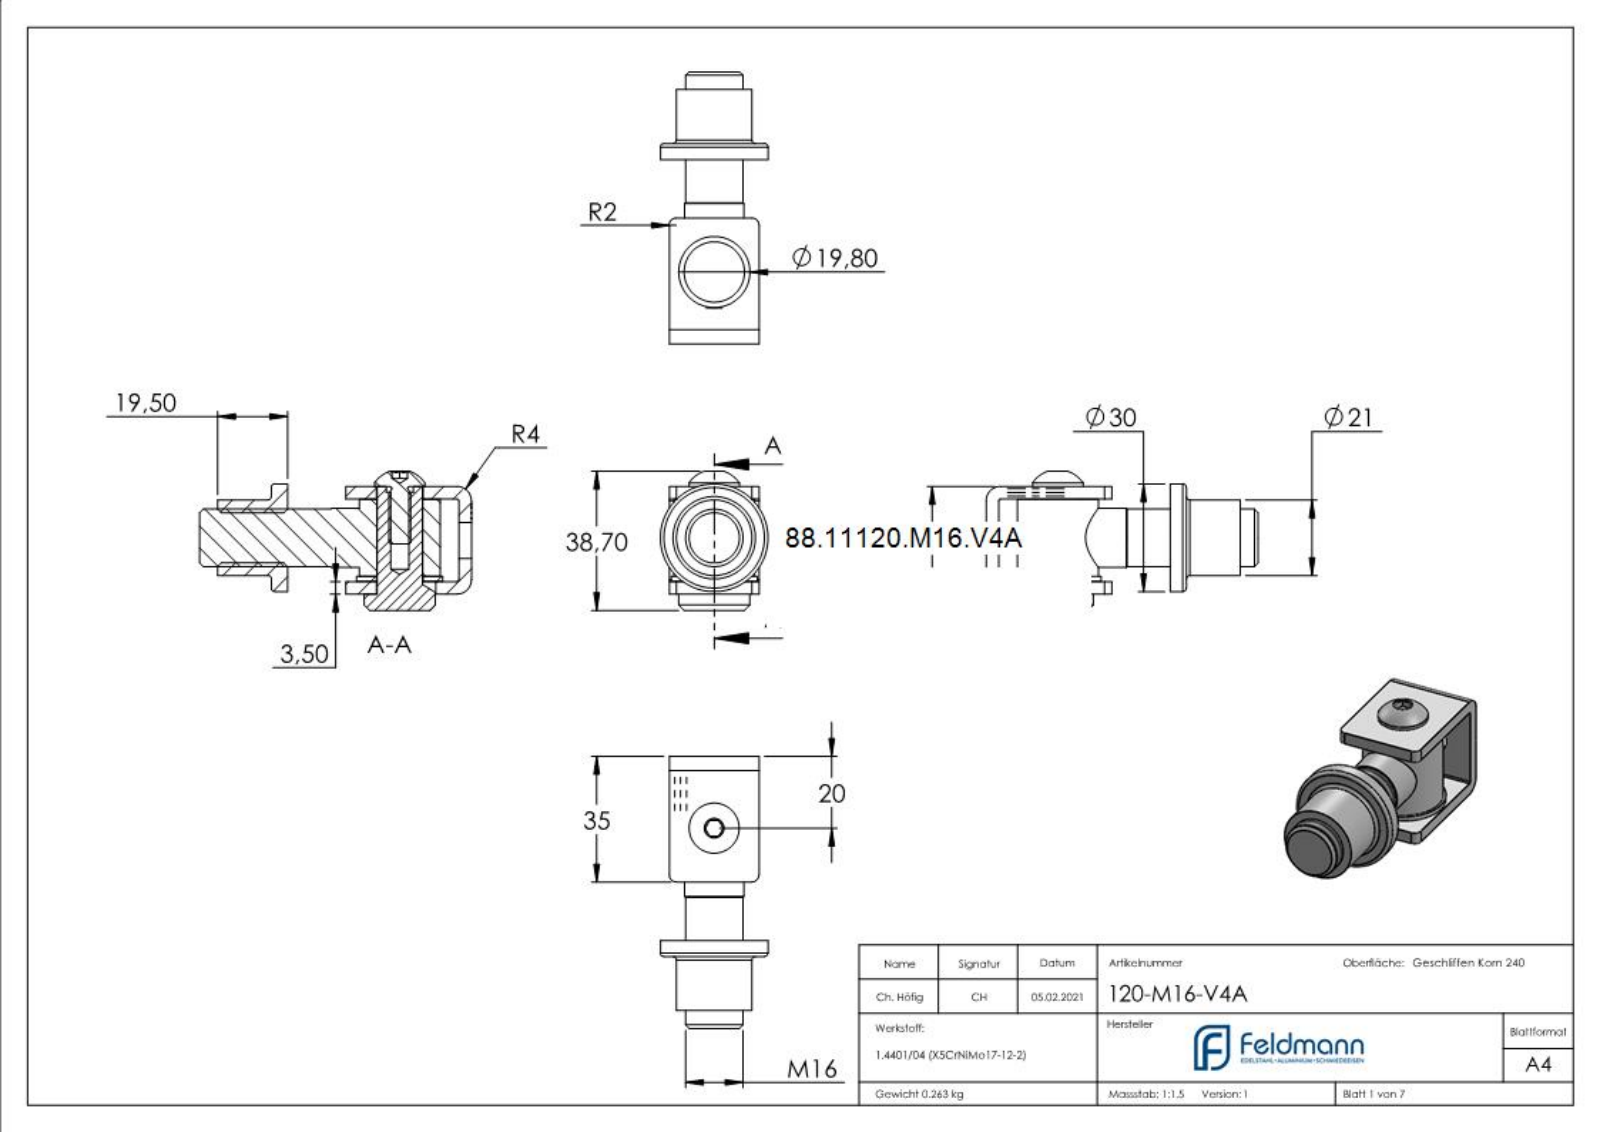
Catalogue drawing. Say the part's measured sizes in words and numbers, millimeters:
The part is named "120-M16-V4A Teil3_120-M12-V4A Teil 3; 120-M16-V4A Teil5_120-M16-V4A Teil5; 120-M16-V4A Teil4_120-M12-V4A Teil 4; ISO7380 - M6x16_ISO7380 - M6x16 (+8 more)". Its 3-D file was written by "SolidWorks 2018 (CONFIG_CONTROL_DESIGN)". It is 6 solids with 380 faces: 210 planar, 45 cylindrical and 125 other. Overall it measures 75.75 by 38.7 by 30 millimeters. Its volume is 32 880 cubic millimeters and its surface area 17 457 square millimeters. Round holes: 1 of diameter 5, 1 of diameter 7.55, 1 of diameter 10, 1 of diameter 12.8, 1 of diameter 13, 1 of diameter 14. Round bosses or shafts: 1 of diameter 30, 1 of diameter 24, 1 of diameter 22.5, 1 of diameter 21, 1 of diameter 19.8, 1 of diameter 16.5, 1 of diameter 16, 1 of diameter 14. Partial cylindrical surfaces (rounded edges, fillets, slot ends): 2 of radius 0.5, 2 of radius 2, 2 of radius 4. The main face-to-face distances are 3.5, 26.5, 30, 23, 22.95, 3.55, 4.95, 26.45, 1.45, 21.55. The hole center spacings are 0.7.
